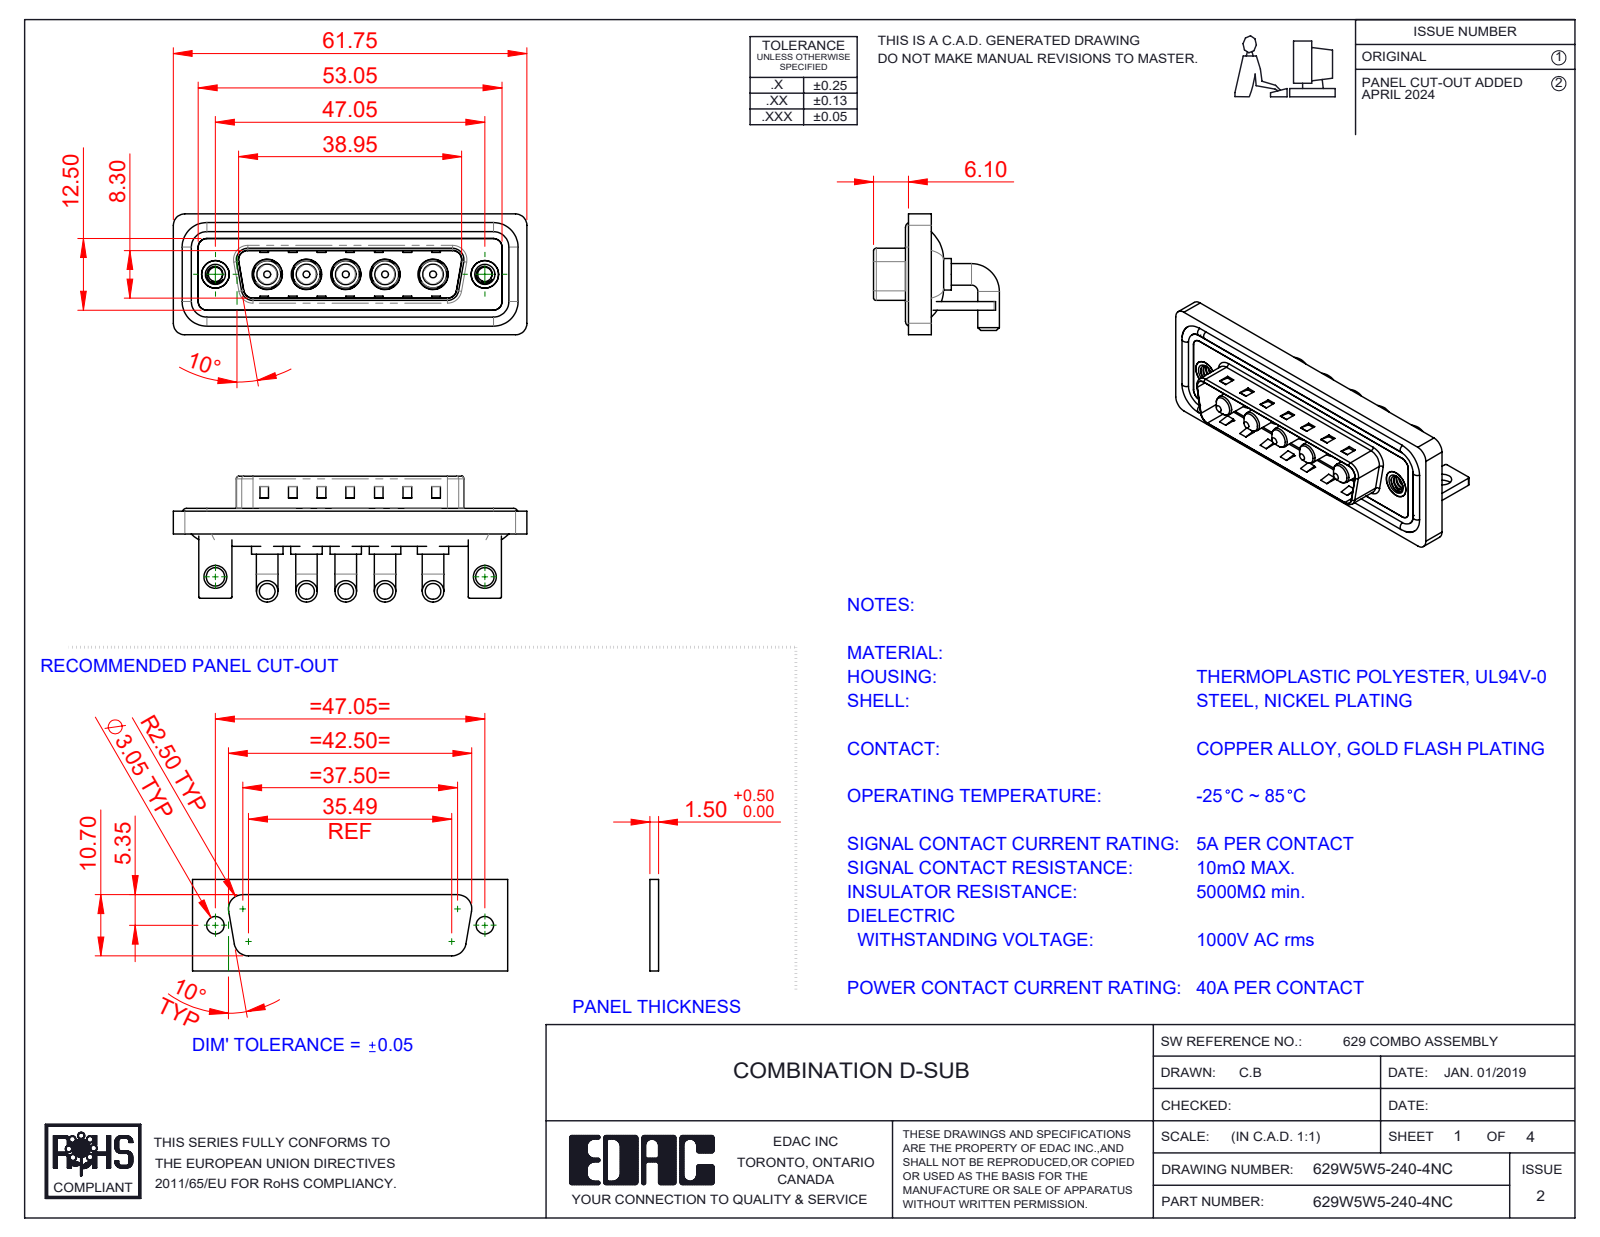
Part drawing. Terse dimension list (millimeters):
name: 629Combo Shell Front_25 Contacts; 629Combo Threaded Rivet_B; 629Combo Housing_5W5; 629W5W5-240-4NC (+4 more)
written by: SolidWorks 2023 (CONFIG_CONTROL_DESIGN)
unit: mm
bodies: 19 solids, 736 faces (279 planar, 311 cylindrical, 146 other)
size: 61.75 × 21.98 × 21.1
volume: 8 439 mm³; area: 13 079 mm²
holes: 5× ⌀4.85, 5× ⌀5.3, 2× ⌀2.5, 2× ⌀3.2, 2× ⌀4, 2× ⌀4.8, 2× ⌀5
bosses: 10× ⌀3.75, 5× ⌀5.5, 5× ⌀5.2, 5× ⌀4.75, 5× ⌀3.6, 4× ⌀1.6, 2× ⌀4.9
rounds: 19× R2, 18× R1.5, 16× R0.25, 9× R0.5, 8× R1.6, 5× R2.1, 4× R0.6, 4× R0.65
face distances: 0.4, 1.5, 2.9, 0.8, 2.1, 3.7, 1.1, 4.5, 4.1, 1.2
hole spacings: 6.86, 13.73, 47.05, 6.85, 6.87, 8.37, 8.38, 9.04
